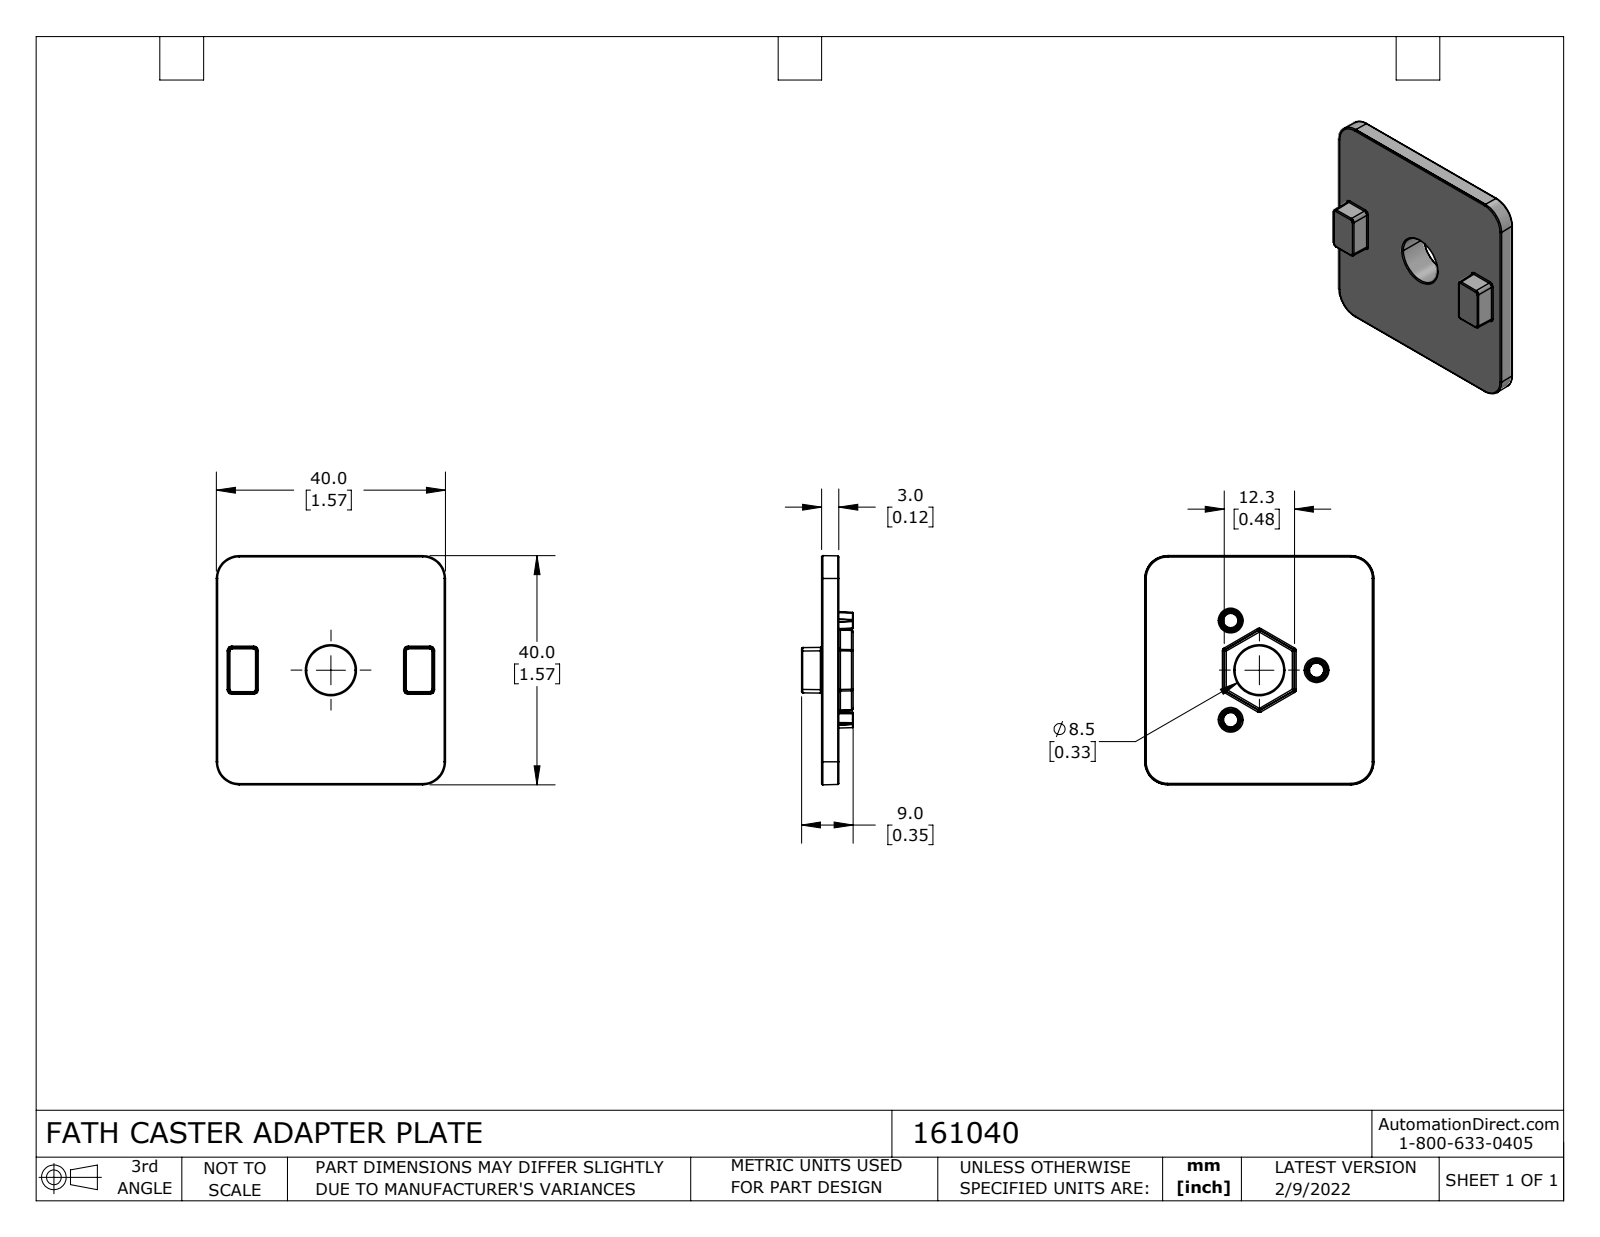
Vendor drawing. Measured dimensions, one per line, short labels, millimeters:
name: 161040
written by: SolidWorks 2021 (CONFIG_CONTROL_DESIGN)
unit: mm
bodies: 1 solid, 356 faces (38 planar, 54 cylindrical, 264 other)
size: 39.99 × 39.99 × 9
volume: 5 065 mm³; area: 3 965 mm²
holes: 1× ⌀8.5
rounds: 20× R0.2, 18× R0.3, 8× R0.6
face distances: 3, 2.5, 5.5, 9, 6.5, 3.5, 24, 7.1, 37.9, 30.8
